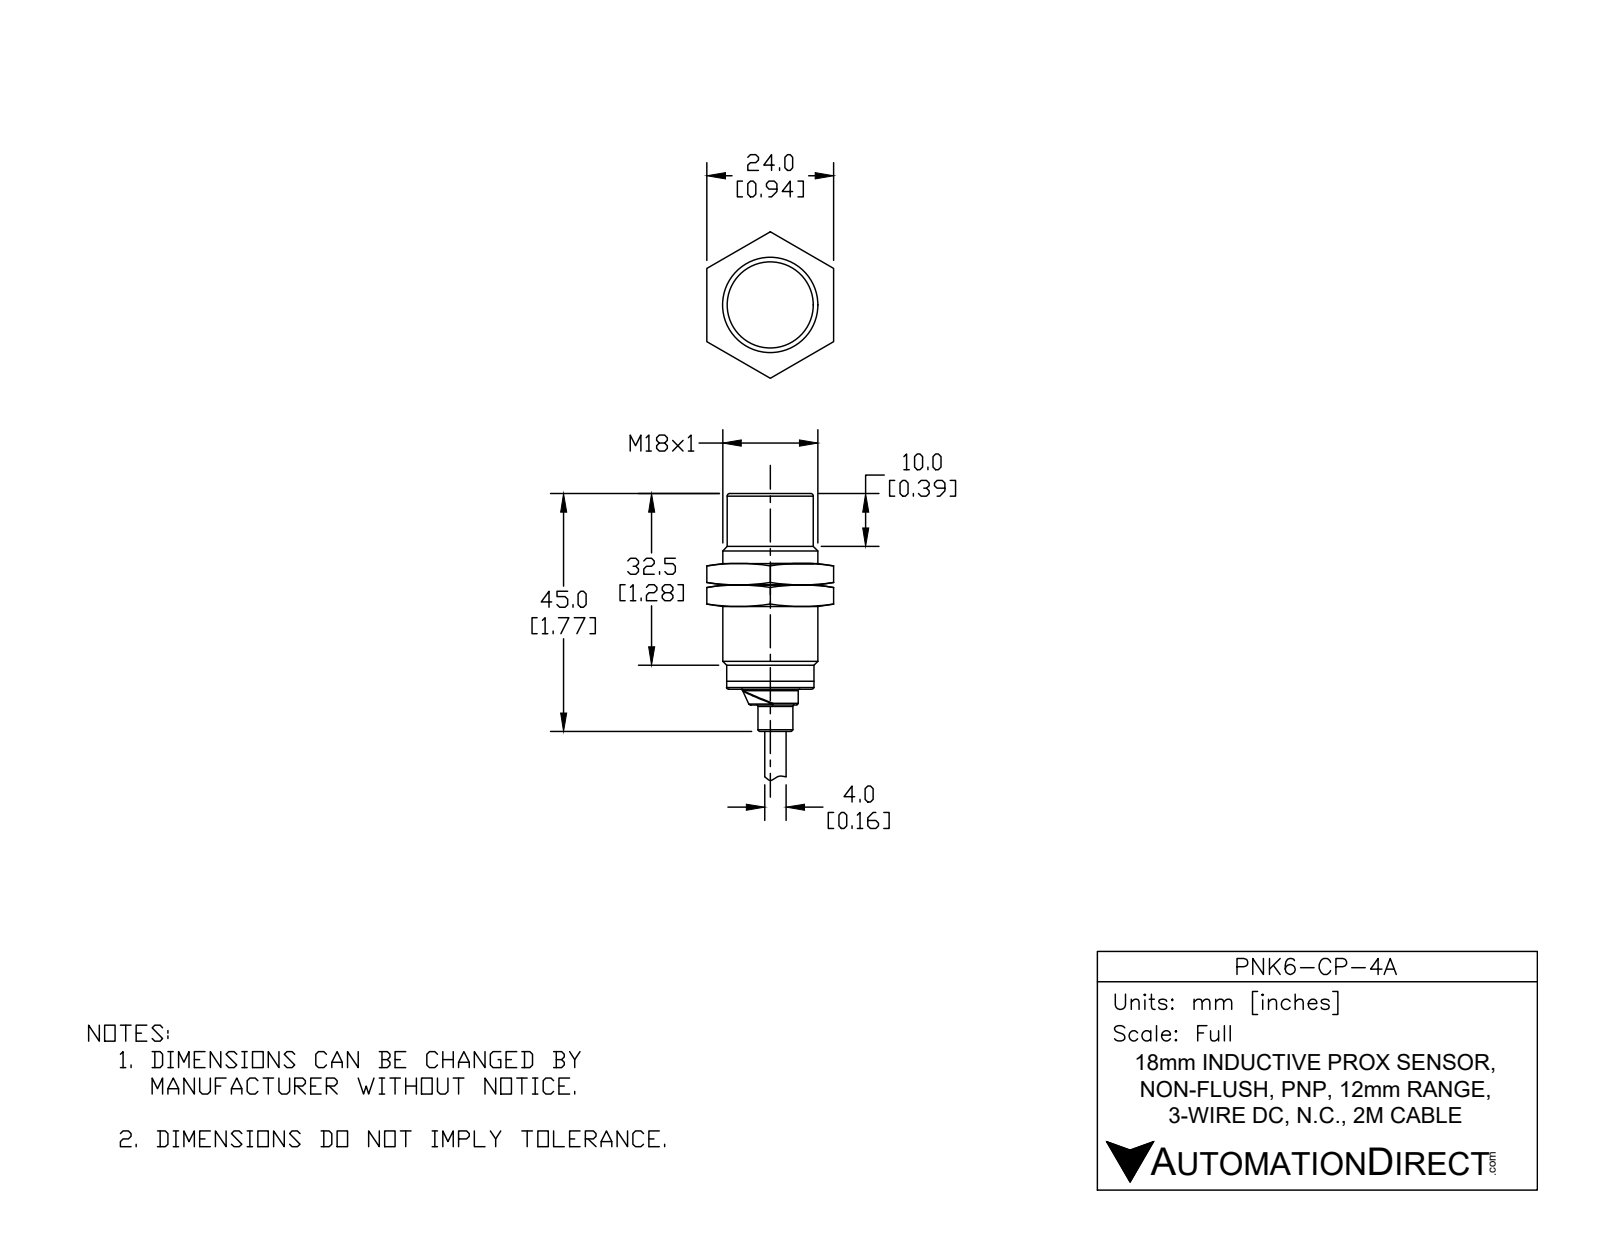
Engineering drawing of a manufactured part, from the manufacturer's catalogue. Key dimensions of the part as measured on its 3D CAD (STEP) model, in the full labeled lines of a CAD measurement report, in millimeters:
Part name (STEP PRODUCT): PNK6-CP-4A
STEP written by: SolidWorks 2017 (AUTOMOTIVE_DESIGN)
Units: millimetres
Bodies: 1 solid, 78 faces (19 planar, 27 cylindrical, 32 other)
Overall size (bounding box): 83.1 × 18 × 18
Volume: 10 000 mm³ · Surface area: 3 500 mm²
Round holes (diameter × count): ⌀4.1 ×1
Round bosses / shafts (diameter × count): ⌀1.2 ×6, ⌀18 ×1, ⌀16.5 ×1, ⌀16.5 ×1, ⌀10.6 ×1, ⌀6.6 ×1, ⌀4 ×1
Partial cylindrical surfaces — rounded edges, fillets, slot ends (radius × count): R3.7 ×1
Main face-to-face distances: 37, 35.5, 1.5, 40, 4.5, 3, 39.2, 3.8, 2.3, 0.8
